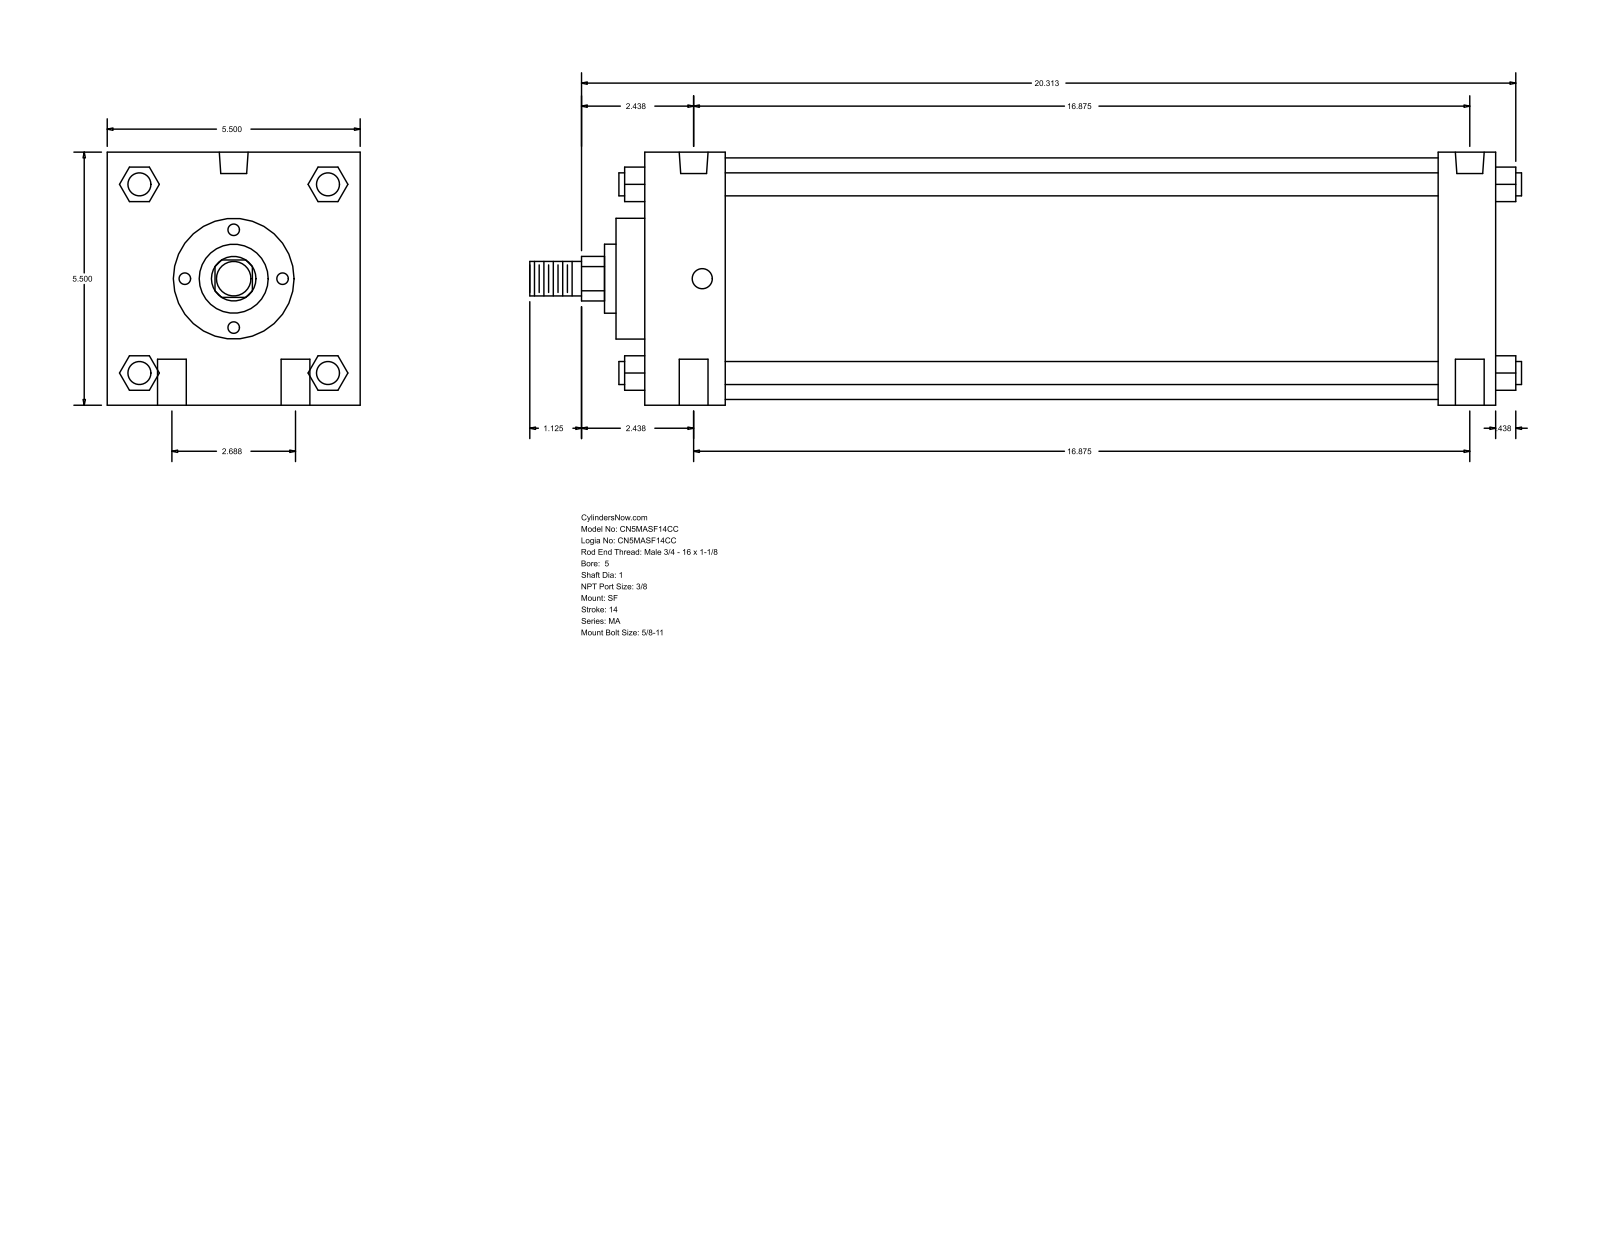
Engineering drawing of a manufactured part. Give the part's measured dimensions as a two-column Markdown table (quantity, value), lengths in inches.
| quantity | value |
| --- | --- |
| part name | MA_SF__0500_1 |
| STEP written by | GSSL Pune (CONFIG_CONTROL_DESIGN) |
| units | inches |
| bodies | 0 solids, 126 faces (95 planar, 31 cylindrical, 0 other) |
| overall size | 21.563 × 5.5 × 5.5 |
| round holes (diameter × count) | 0.625 × 4, 0.437 × 2, 0.627 × 2 |
| round bosses / shafts (diameter × count) | 0.5 × 4, 5.25 × 1, 2.625 × 1, 1.5 × 1, 1 × 1, 0.75 × 1 |
| partial cylindrical surfaces (radius × count) | 0.484 × 1 |
| main face-to-face distances | 5.5, 18.5, 1.75, 17.25, 15.5, 16.75, 1.25, 0.625, 2.375, 17.875 |
| hole center spacings | 1.344, 16.929, 16.875, 2.687, 17.088, 16.5 |
